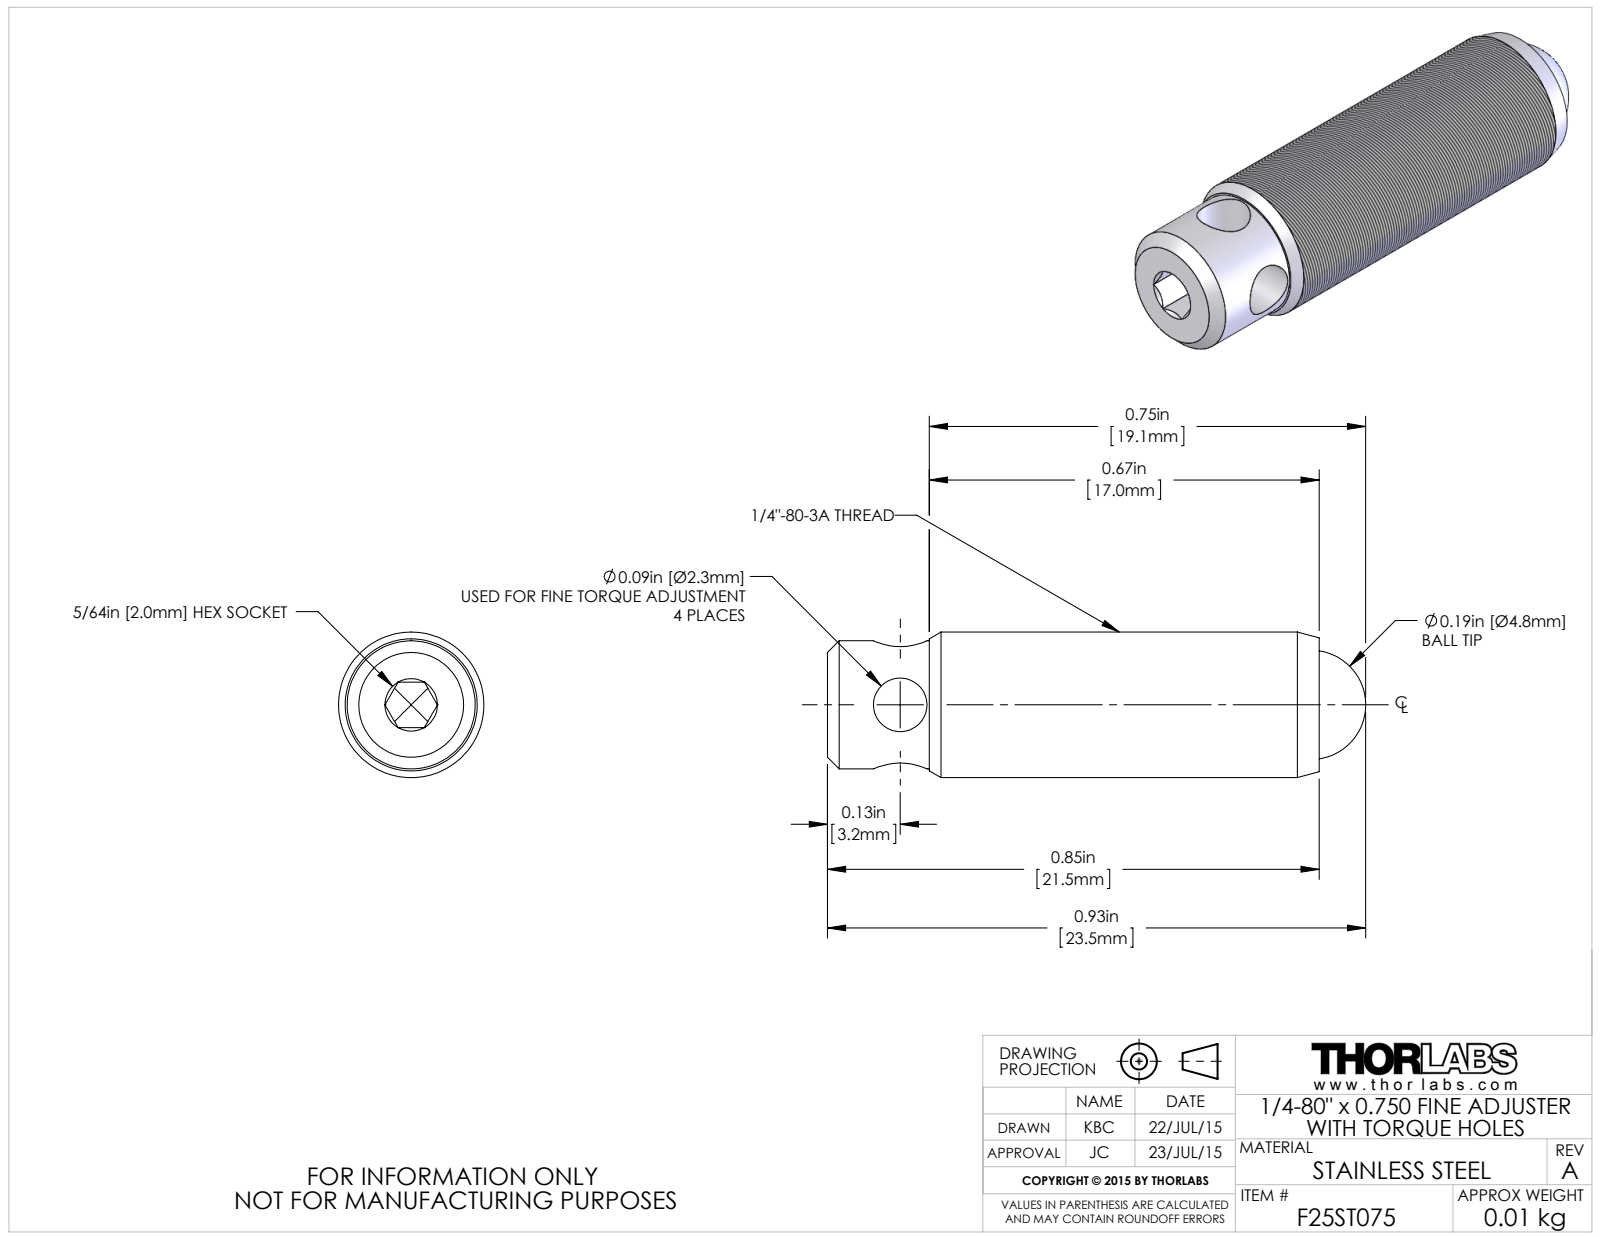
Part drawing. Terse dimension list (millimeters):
name: TTN045069-E0W
written by: SolidWorks 2014 (AUTOMOTIVE_DESIGN)
unit: mm
bodies: 2 solids, 40 faces (9 planar, 14 cylindrical, 17 other)
size: 23.5 × 6.4 × 6.4
volume: 620 mm³; area: 610 mm²
holes: 2× ⌀2.3, 1× ⌀4.8
bosses: 1× ⌀6.4, 1× ⌀5.6
face distances: 21.5, 2, 4.4, 17
